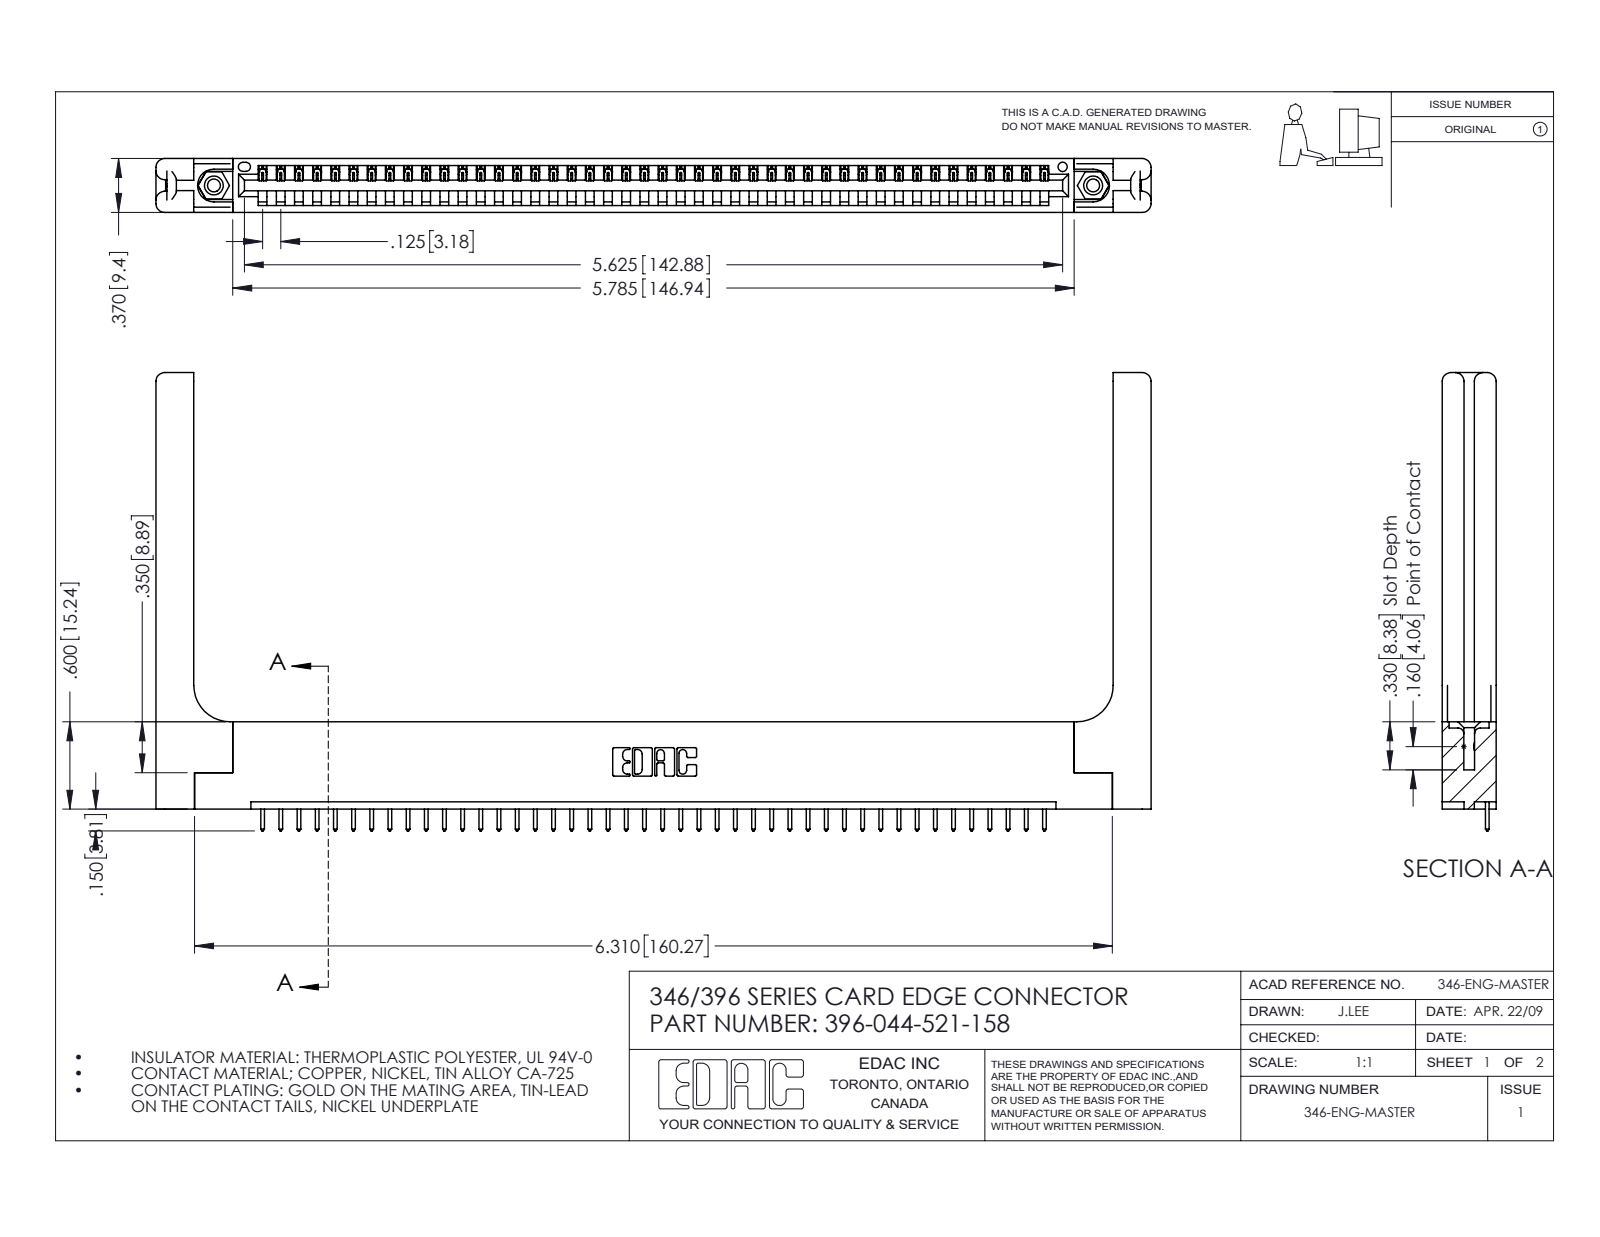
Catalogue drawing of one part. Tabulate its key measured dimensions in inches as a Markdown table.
| quantity | value |
| --- | --- |
| part name | 346 Part_Flush Mounting Lugs - 0.156 Dia-TH; 345-250-001_345-250-001-102; 346-220-058_345-220-058; 396-044-521-158 (+1 more) |
| STEP written by | SolidWorks 2016 (CONFIG_CONTROL_DESIGN) |
| units | inches |
| bodies | 49 solids, 2930 faces (1984 planar, 886 cylindrical, 60 other) |
| overall size | 6.841 × 3.15 × 0.37 |
| volume | 1.467 in³ |
| surface area | 39.28 in² |
| round holes (diameter × count) | 0.089 × 2, 0.125 × 2, 0.156 × 2, 0.064 × 1 |
| round bosses / shafts (diameter × count) | 0.155 × 2 |
| partial cylindrical surfaces (radius × count) | 0.006 × 88, 0.01 × 88, 0.01 × 22, 0.06 × 16, 0.007 × 6, 0.031 × 6, 0.026 × 3, 0.03 × 2 |
| main face-to-face distances | 0.37, 0.048, 0.322, 0.072, 0.148, 0.15, 0.25, 0.298, 0.025, 0.222 |
| hole center spacings | 0.246, 5.836, 6.045 |
